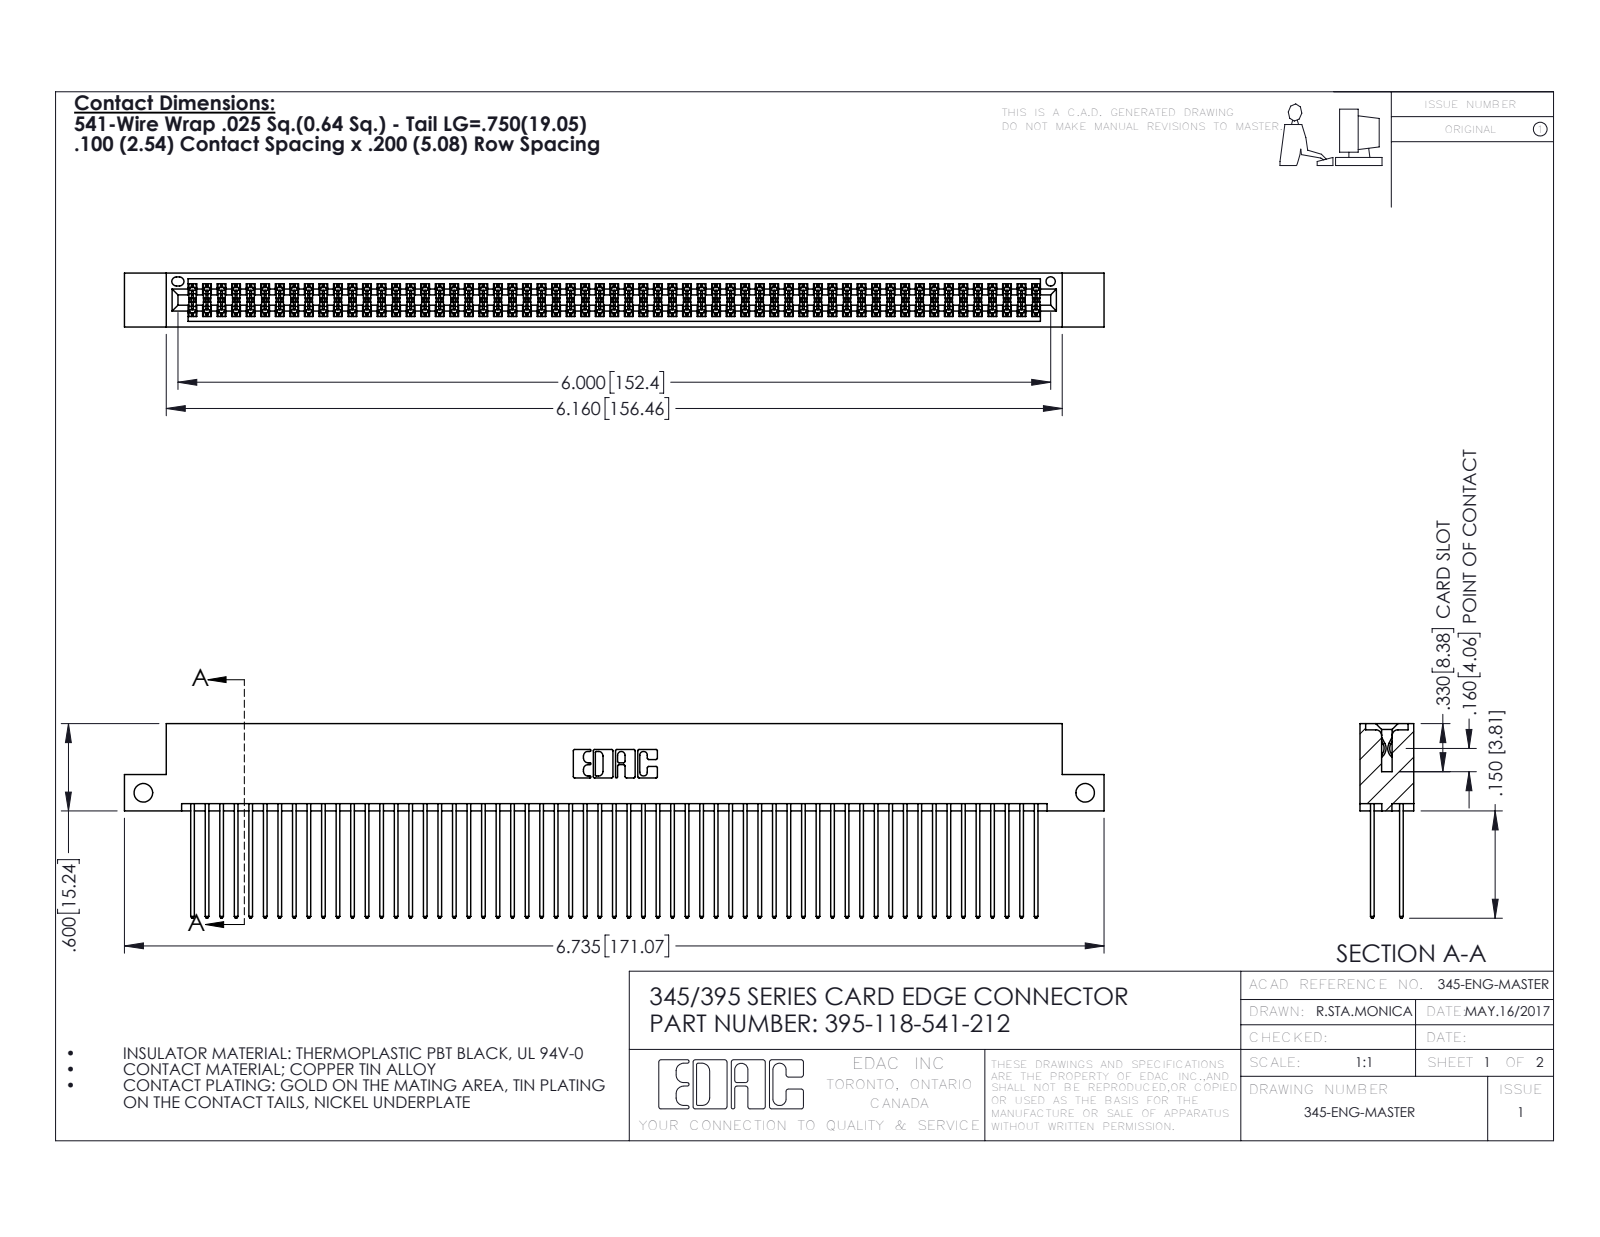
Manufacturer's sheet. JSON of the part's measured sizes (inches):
{"part_name": "345 Part_Flush Mounting Lugs - Side Mount; 345-292-001_345-293-141; 395-118-541-212", "step_written_by": "SolidWorks 2016 (CONFIG_CONTROL_DESIGN)", "units": "inches", "bodies": {"solids": 119, "faces": 6026, "planar": 3974, "cylindrical": 2052, "other": 0}, "overall_size": [6.735, 1.337, 0.37], "volume_in3": 1.06, "surface_area_in2": 45.02, "round_holes": [[0.128, 2], [0.064, 1]], "partial_cylinders_radius": [[0.006, 177], [0.01, 118], [0.01, 22], [0.007, 6], [0.031, 6], [0.026, 3], [0.014, 2], [0.019, 2]], "face_to_face_distances": [0.298, 0.072, 0.2, 0.098, 0.272, 0.025, 0.225, 0.37, 0.175, 0.149], "hole_center_spacings": [6.475]}
